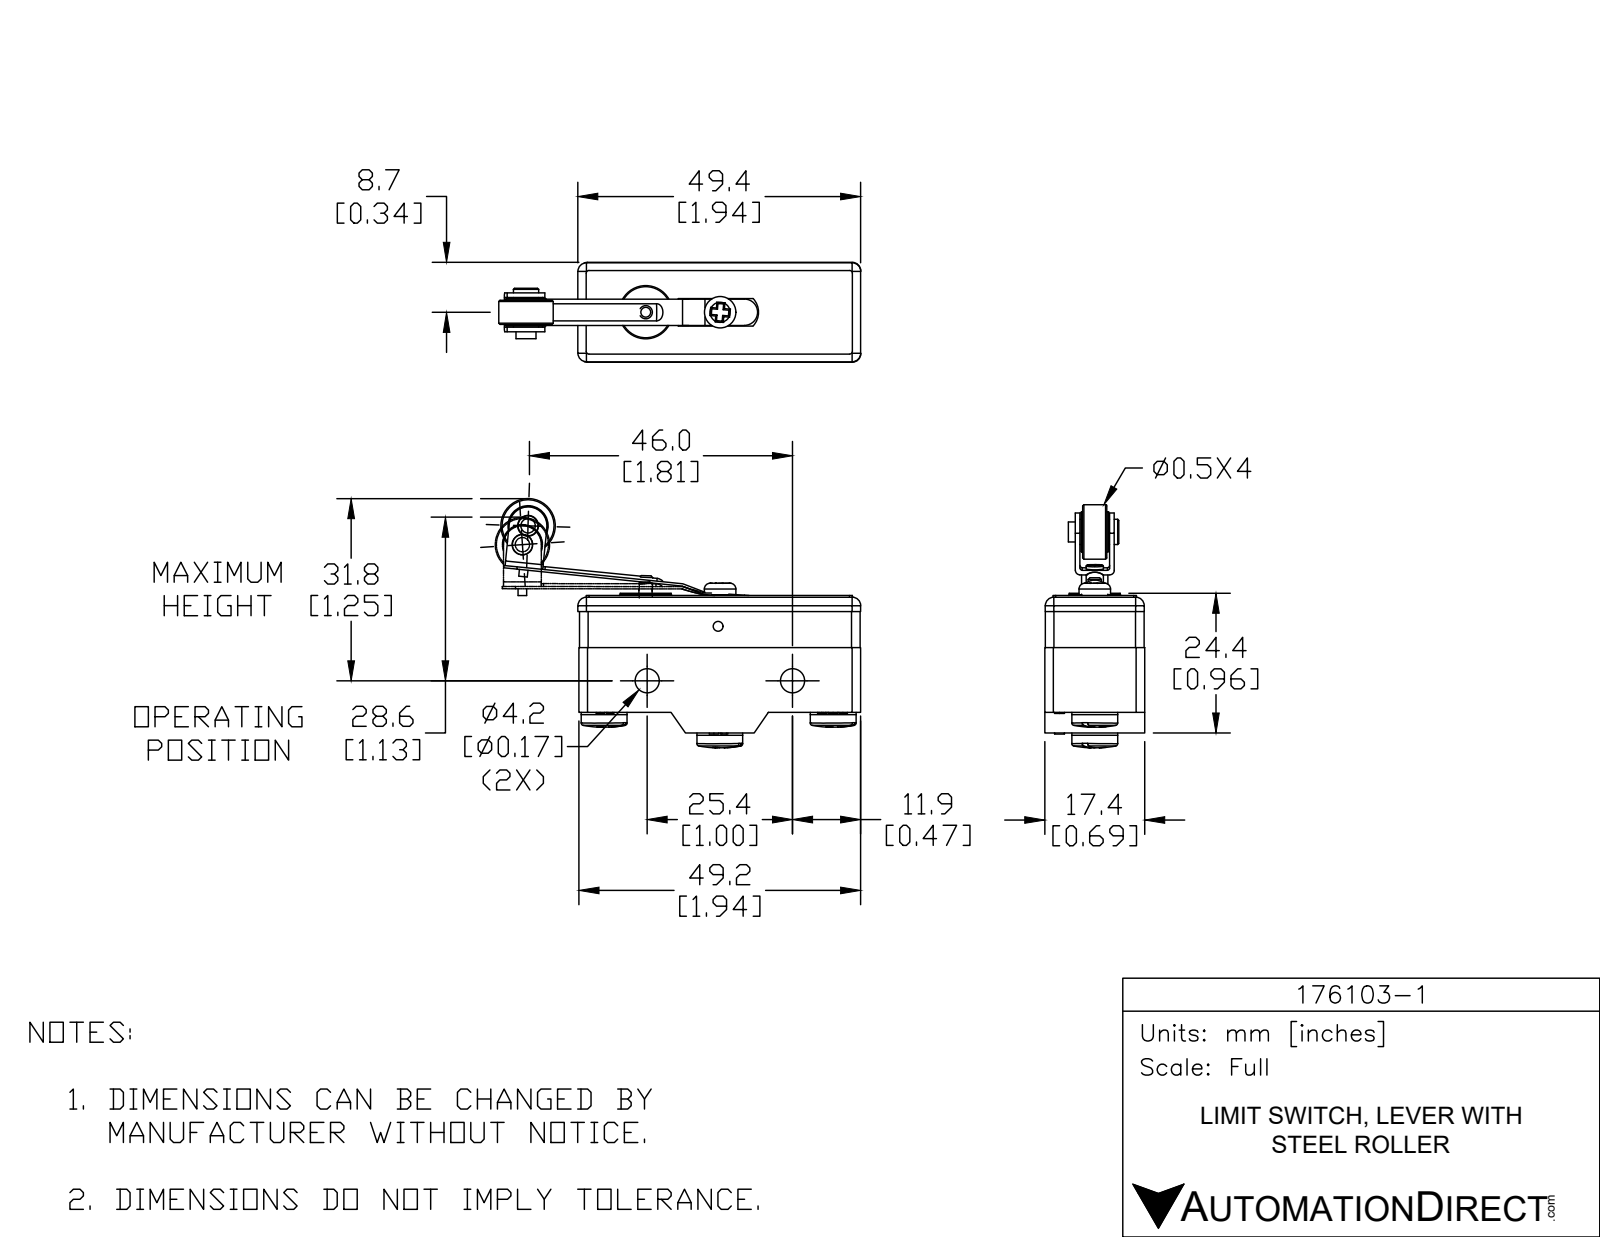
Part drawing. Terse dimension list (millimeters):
name: 176-MS (Screw Terminal)-Roller Lever
written by: SolidWorks 2018 (AUTOMOTIVE_DESIGN)
unit: mm
bodies: 15 solids, 578 faces (244 planar, 151 cylindrical, 183 other)
size: 64.3 × 42.4 × 17.4
volume: 17 570 mm³; area: 9 600 mm²
holes: 3× ⌀3.8, 3× ⌀6, 2× ⌀2.5, 2× ⌀4.2, 1× ⌀1.5, 1× ⌀1.6, 1× ⌀1.7, 1× ⌀2.4, 1× ⌀3.1, 1× ⌀3.6, 1× ⌀4.5, 1× ⌀4.9
bosses: 3× ⌀8, 2× ⌀3, 1× ⌀9.5, 1× ⌀8.9, 1× ⌀7, 1× ⌀5.5, 1× ⌀4.4, 1× ⌀3.5
rounds: 16× R1.5, 12× R0.3, 9× R0.2, 4× R0.5, 3× R2.9, 2× R0.4, 2× R0.8, 2× R2.3
face distances: 17.3, 17.6, 17.4, 2.8, 20.4, 0.4, 3.6, 17.2, 21.2, 24
hole spacings: 7.2, 13, 13, 15.6, 16.1, 19.8, 19.8, 20.2
